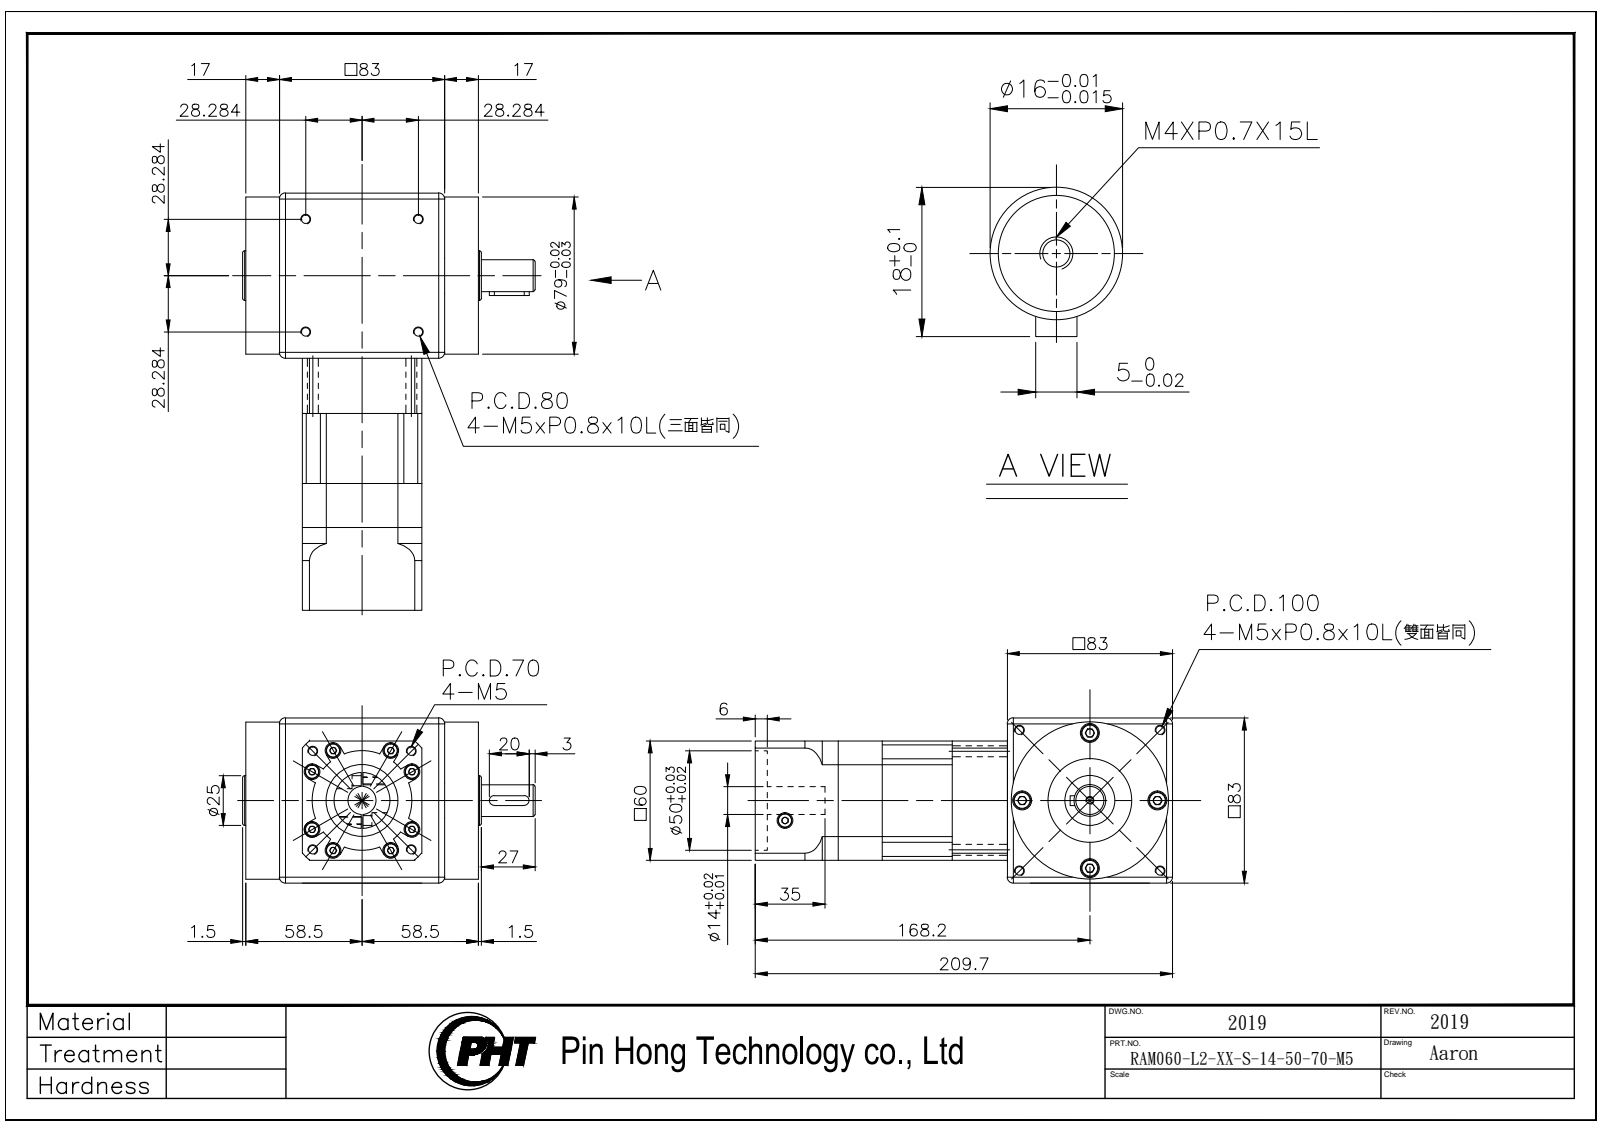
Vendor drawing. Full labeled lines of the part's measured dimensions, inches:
Part name (STEP PRODUCT): RAM060-L2-XX-S-14-50-70-M5_2019
STEP written by: SolidWorks 2016 (AUTOMOTIVE_DESIGN)
Units: inches
Bodies: 6 solids, 697 faces (325 planar, 240 cylindrical, 132 other)
Overall size (bounding box): 8.256 × 5.787 × 3.268
Volume: 68.83 in³ · Surface area: 209.1 in²
Round holes (diameter × count): ⌀0.165 ×16, ⌀0.315 ×10, ⌀0.177 ×8, ⌀0.217 ×8, ⌀0.374 ×4, ⌀0.13 ×1, ⌀0.157 ×1, ⌀0.551 ×1, ⌀1.417 ×1
Round bosses / shafts (diameter × count): ⌀0.335 ×8, ⌀0.276 ×8, ⌀3.11 ×1, ⌀2.165 ×1, ⌀1.654 ×1, ⌀1.102 ×1, ⌀0.984 ×1, ⌀0.63 ×1
Partial cylindrical surfaces — rounded edges, fillets, slot ends (radius × count): R0.197 ×4, R0.098 ×2, R0.984 ×1, R1.378 ×1, R1.575 ×1, R2.25 ×1
Main face-to-face distances: 2.815, 0.453, 3.268, 2.362, 1.091, 2.258, 3.348, 0.872, 1.386, 2.476
Hole centre spacings: 1.142, 0.404, 0.557, 1.545, 1.615, 1.689, 2.004, 2.093
